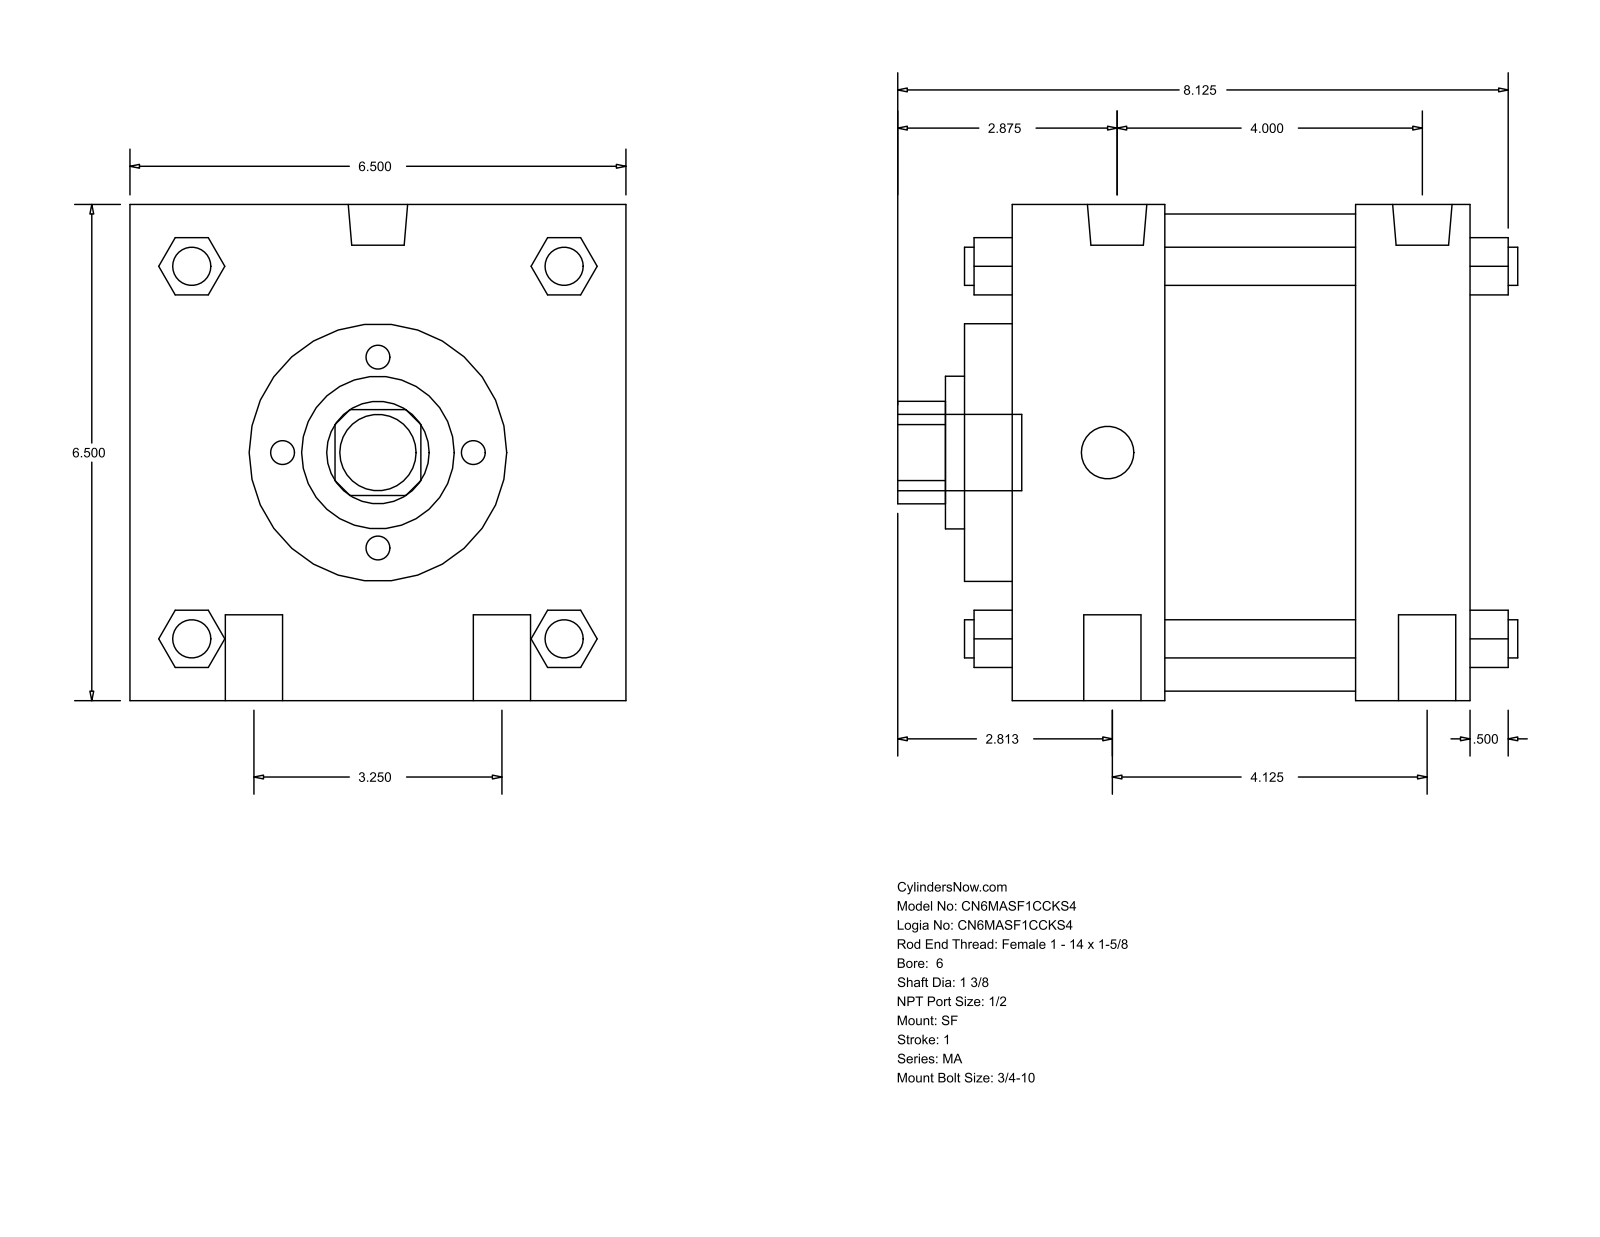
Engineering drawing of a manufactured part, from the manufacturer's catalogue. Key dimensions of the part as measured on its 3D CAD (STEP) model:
Part name (STEP PRODUCT): MA_SF__0600_1.375
STEP written by: GSSL Pune (CONFIG_CONTROL_DESIGN)
Units: millimetres
Bodies: 0 solids, 126 faces (95 planar, 31 cylindrical, 0 other)
Overall size (bounding box): 206.38 × 165.1 × 165.1
Round holes (diameter × count): ⌀34.92 ×1, ⌀50.8 ×1, ⌀85.72 ×1, ⌀158.75 ×1
Round bosses / shafts (diameter × count): ⌀19.05 ×4, ⌀12.7 ×4, ⌀19.77 ×2, ⌀17.46 ×2, ⌀25.4 ×1
Partial cylindrical surfaces — rounded edges, fillets, slot ends (radius × count): R17.06 ×1
Main face-to-face distances: 165.1, 152.4, 114.3, 63.5, 50.8, 38.1, 101.6, 15.87, 66.67, 130.17
